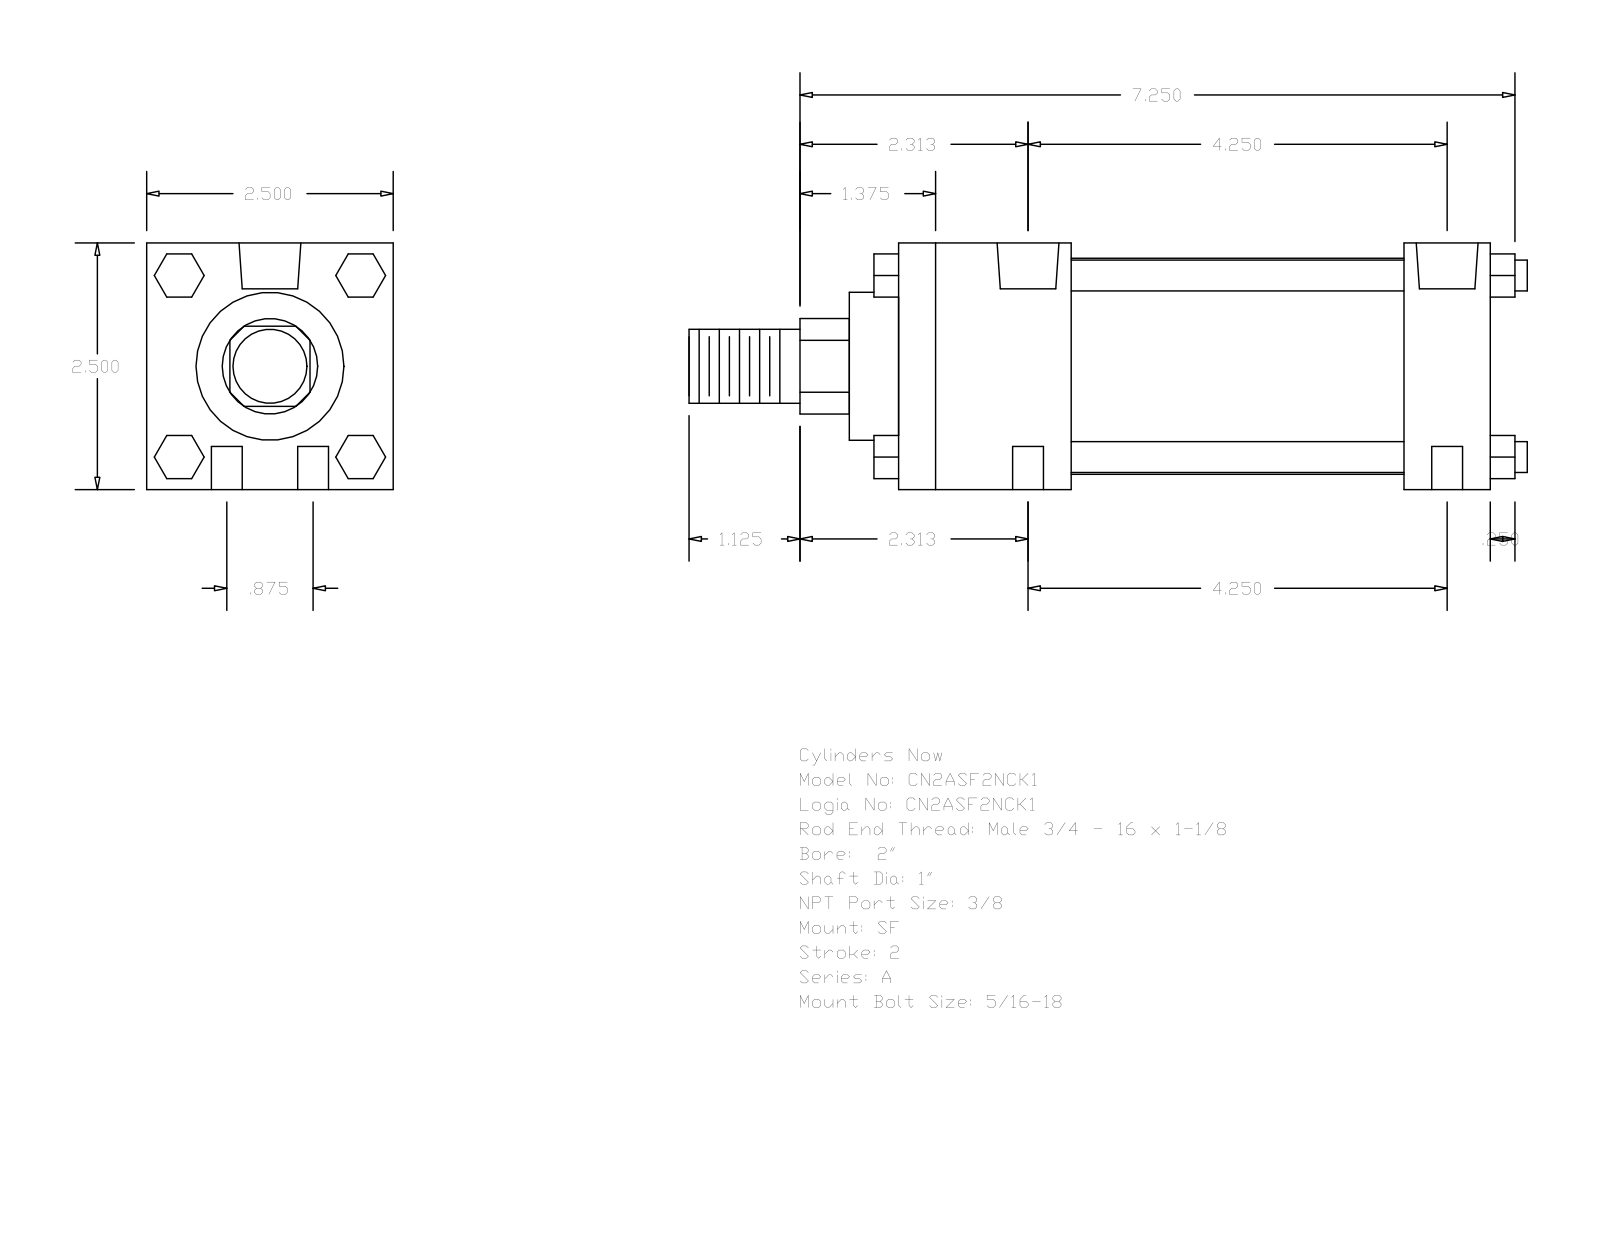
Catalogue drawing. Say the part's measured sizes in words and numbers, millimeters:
The part is named "A_SF__0200_1". Its 3-D file was written by "GSSL Pune (CONFIG_CONTROL_DESIGN)". It is 0 solids with 124 faces: 94 planar, 30 cylindrical and 0 other. Overall it measures 215.9 by 63.5 by 63.5 millimeters. Round holes: 4 of diameter 7.94, 2 of diameter 5.56, 2 of diameter 15.93. Round bosses or shafts: 4 of diameter 7.94, 1 of diameter 55.63, 1 of diameter 38.1, 1 of diameter 25.4, 1 of diameter 19.05. Partial cylindrical surfaces (rounded edges, fillets, slot ends): 1 of radius 12.29. The main face-to-face distances are 63.5, 152.4, 130.17, 22.23, 44.45, 85.72, 107.95, 12.7, 165.1, 6.35. The hole center spacings are 11.11, 108.52, 107.95, 22.22, 110.21, 102.38.
